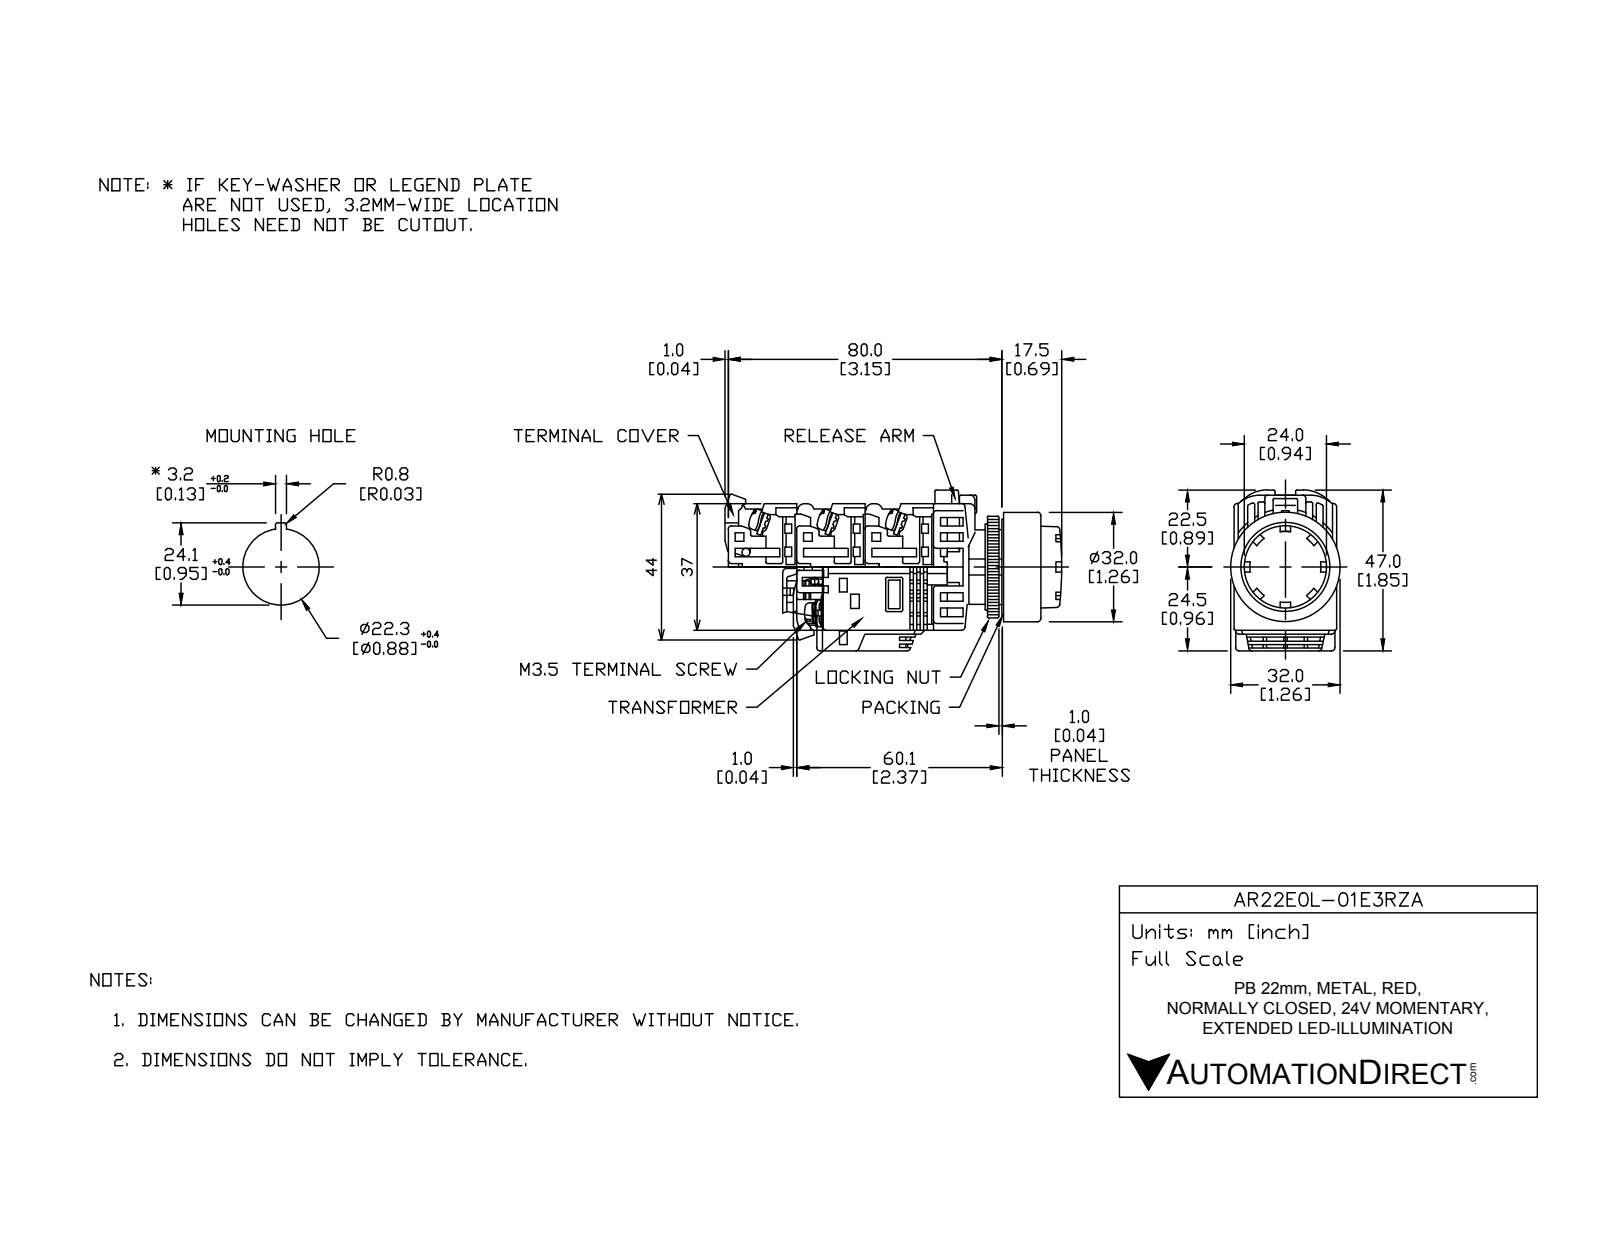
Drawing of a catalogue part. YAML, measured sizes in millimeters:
part_name: "AR22E0L-01E3RZA"
step_written_by: "SolidWorks 2017 (AUTOMOTIVE_DESIGN)"
units: millimeters
bodies: {solids: 18, faces: 475, planar: 329, cylindrical: 111, other: 35}
overall_size: [59.25, 43.81, 32]
volume: 39258
surface_area: 24550
round_holes:
  - {diameter: 21.8, count: 1}
  - {diameter: 22, count: 1}
  - {diameter: 25, count: 1}
  - {diameter: 31, count: 1}
round_bosses_or_shafts:
  - {diameter: 5, count: 4}
  - {diameter: 32, count: 1}
  - {diameter: 30.5, count: 1}
  - {diameter: 29.8, count: 1}
  - {diameter: 24, count: 1}
  - {diameter: 23.8, count: 1}
  - {diameter: 21.75, count: 1}
  - {diameter: 17, count: 1}
partial_cylinders:
  - {radius: 0.5, count: 39}
  - {radius: 1.75, count: 8}
  - {radius: 5, count: 4}
  - {radius: 4, count: 2}
  - {radius: 16.59, count: 1}
  - {radius: 17.59, count: 1}
face_to_face_distances: [1, 18, 28.5, 48.5, 20, 29, 3, 2, 21, 0.5]
